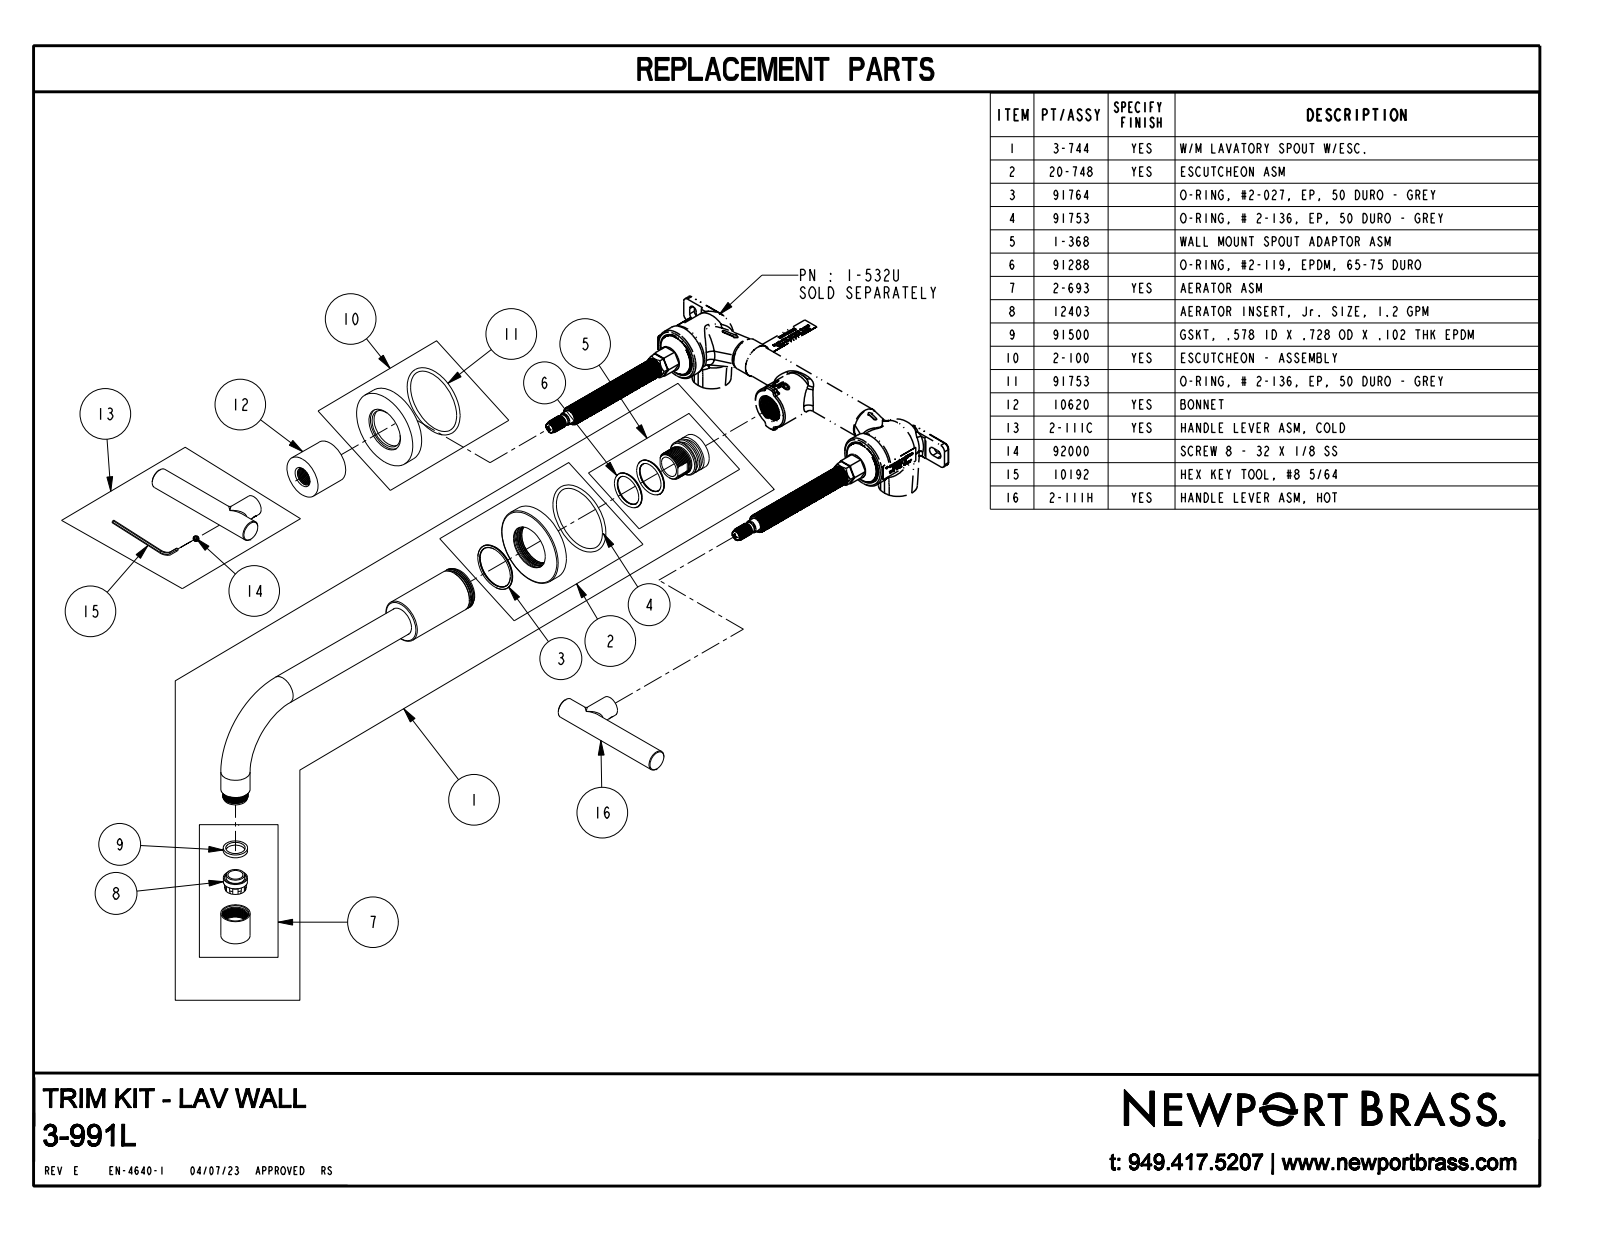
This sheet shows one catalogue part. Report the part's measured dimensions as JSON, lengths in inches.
{"part_name": "3-991L_SW0001", "step_written_by": "CREO PARAMETRIC BY PTC INC, 2018400 (CONFIG_CONTROL_DESIGN)", "units": "inches", "bodies": {"solids": 5, "faces": 139, "planar": 49, "cylindrical": 62, "other": 28}, "overall_size": [13.852, 9.937, 4.628], "volume_in3": 19.34, "surface_area_in2": 99.75, "round_holes": [[0.339, 1], [0.42, 1]], "round_bosses_or_shafts": [[2.375, 3], [0.625, 3], [1.313, 2], [0.875, 2], [1.312, 1]], "partial_cylinders_radius": [[0.187, 1]], "face_to_face_distances": [0.375, 1.483, 1.108, 2.5, 2.125, 1.017, 3.875, 9.977, 1.503, 1.128]}
